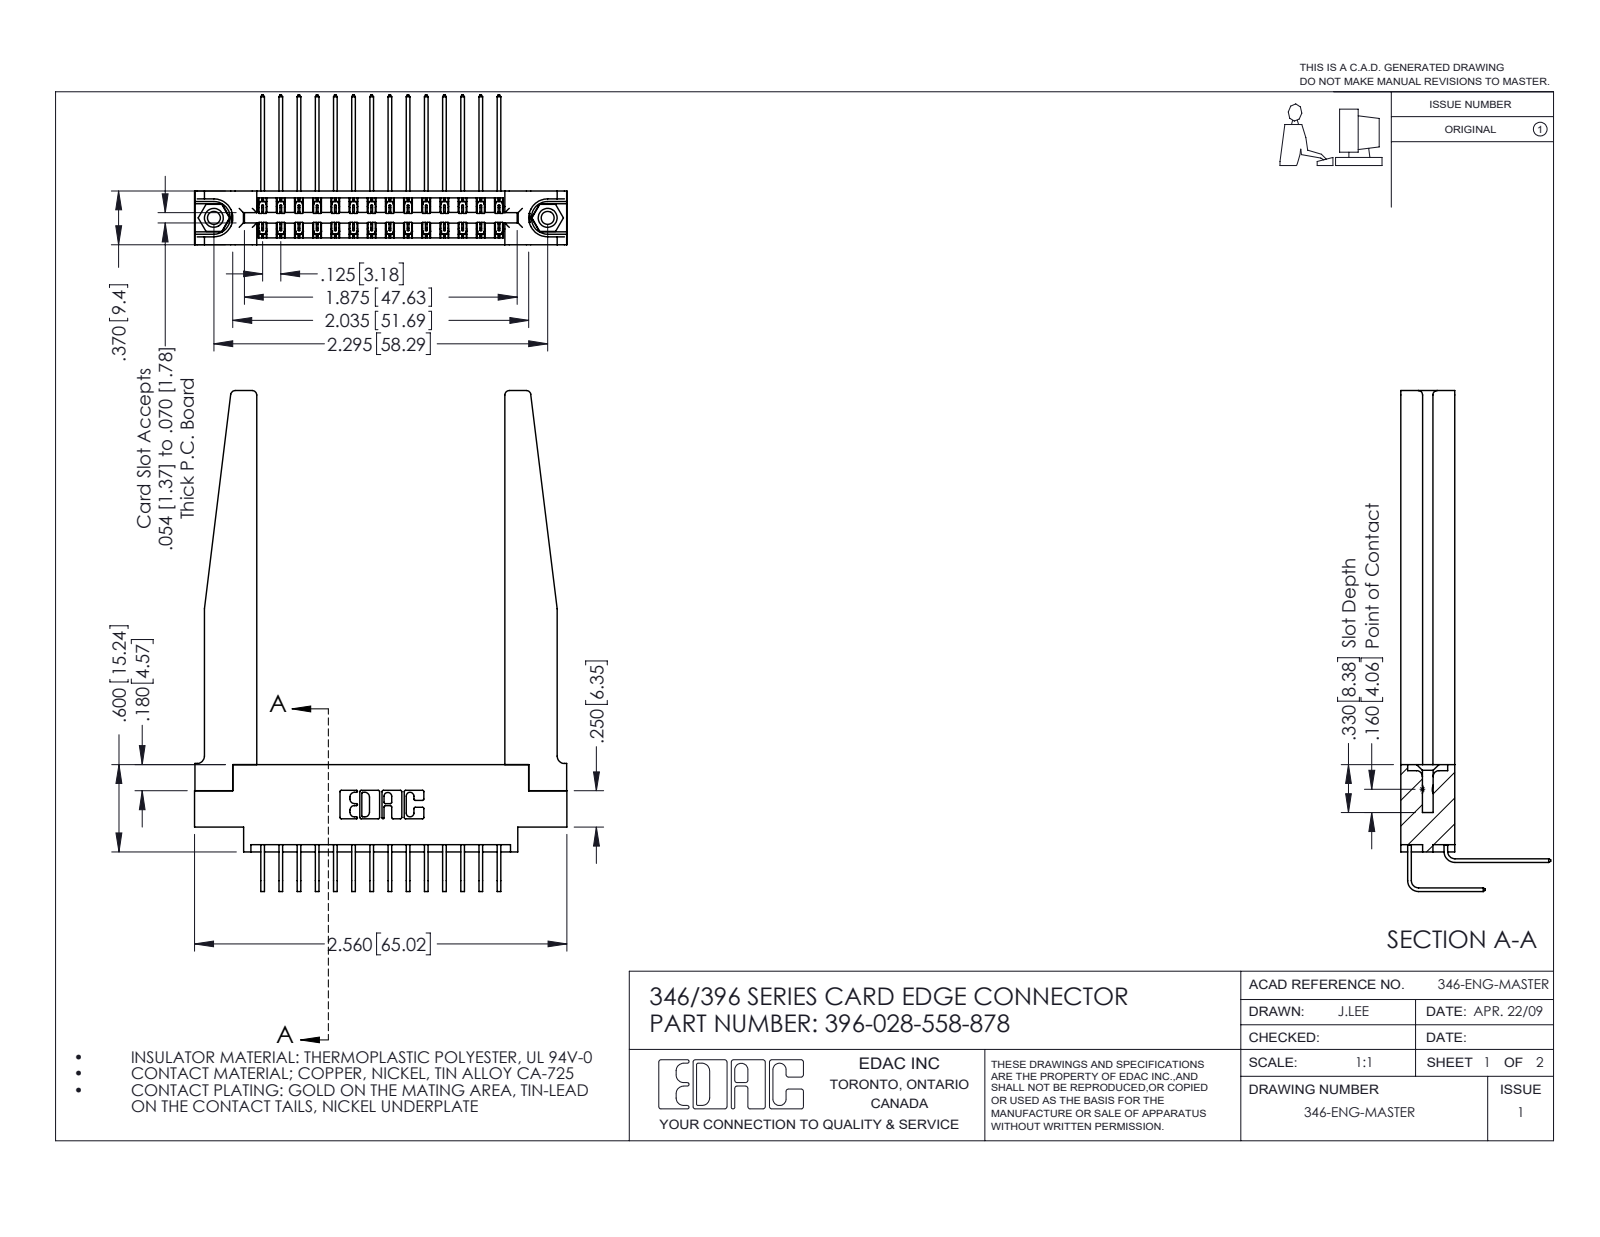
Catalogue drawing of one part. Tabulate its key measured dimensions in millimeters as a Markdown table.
| quantity | value |
| --- | --- |
| part name | 346-220-078_345-220-078; 346 Part_0.170 Offset - 0.156 Dia-TH; 345-292-001_558 Tail - 2; 345-250-001_345-250-001-102 (+2 more) |
| STEP written by | SolidWorks 2016 (CONFIG_CONTROL_DESIGN) |
| units | millimeters |
| bodies | 33 solids, 1872 faces (1258 planar, 562 cylindrical, 52 other) |
| overall size | 87.5 × 65 × 26.2 |
| volume | 13 000 mm³ |
| surface area | 15 480 mm² |
| round holes (diameter × count) | 2.3 × 2, 3.2 × 2, 4 × 2, 1.6 × 1 |
| round bosses / shafts (diameter × count) | 3.9 × 2 |
| partial cylindrical surfaces (radius × count) | 0.2 × 42, 0.3 × 22, 0.8 × 8, 0.2 × 6, 0.8 × 6, 1.3 × 4, 0.7 × 3, 0.4 × 2 |
| main face-to-face distances | 9.4, 1.8, 1.2, 8.2, 3.8, 3.8, 6.4, 0.6, 7.6, 5.6 |
| hole center spacings | 6.2, 53.1, 58.3 |
